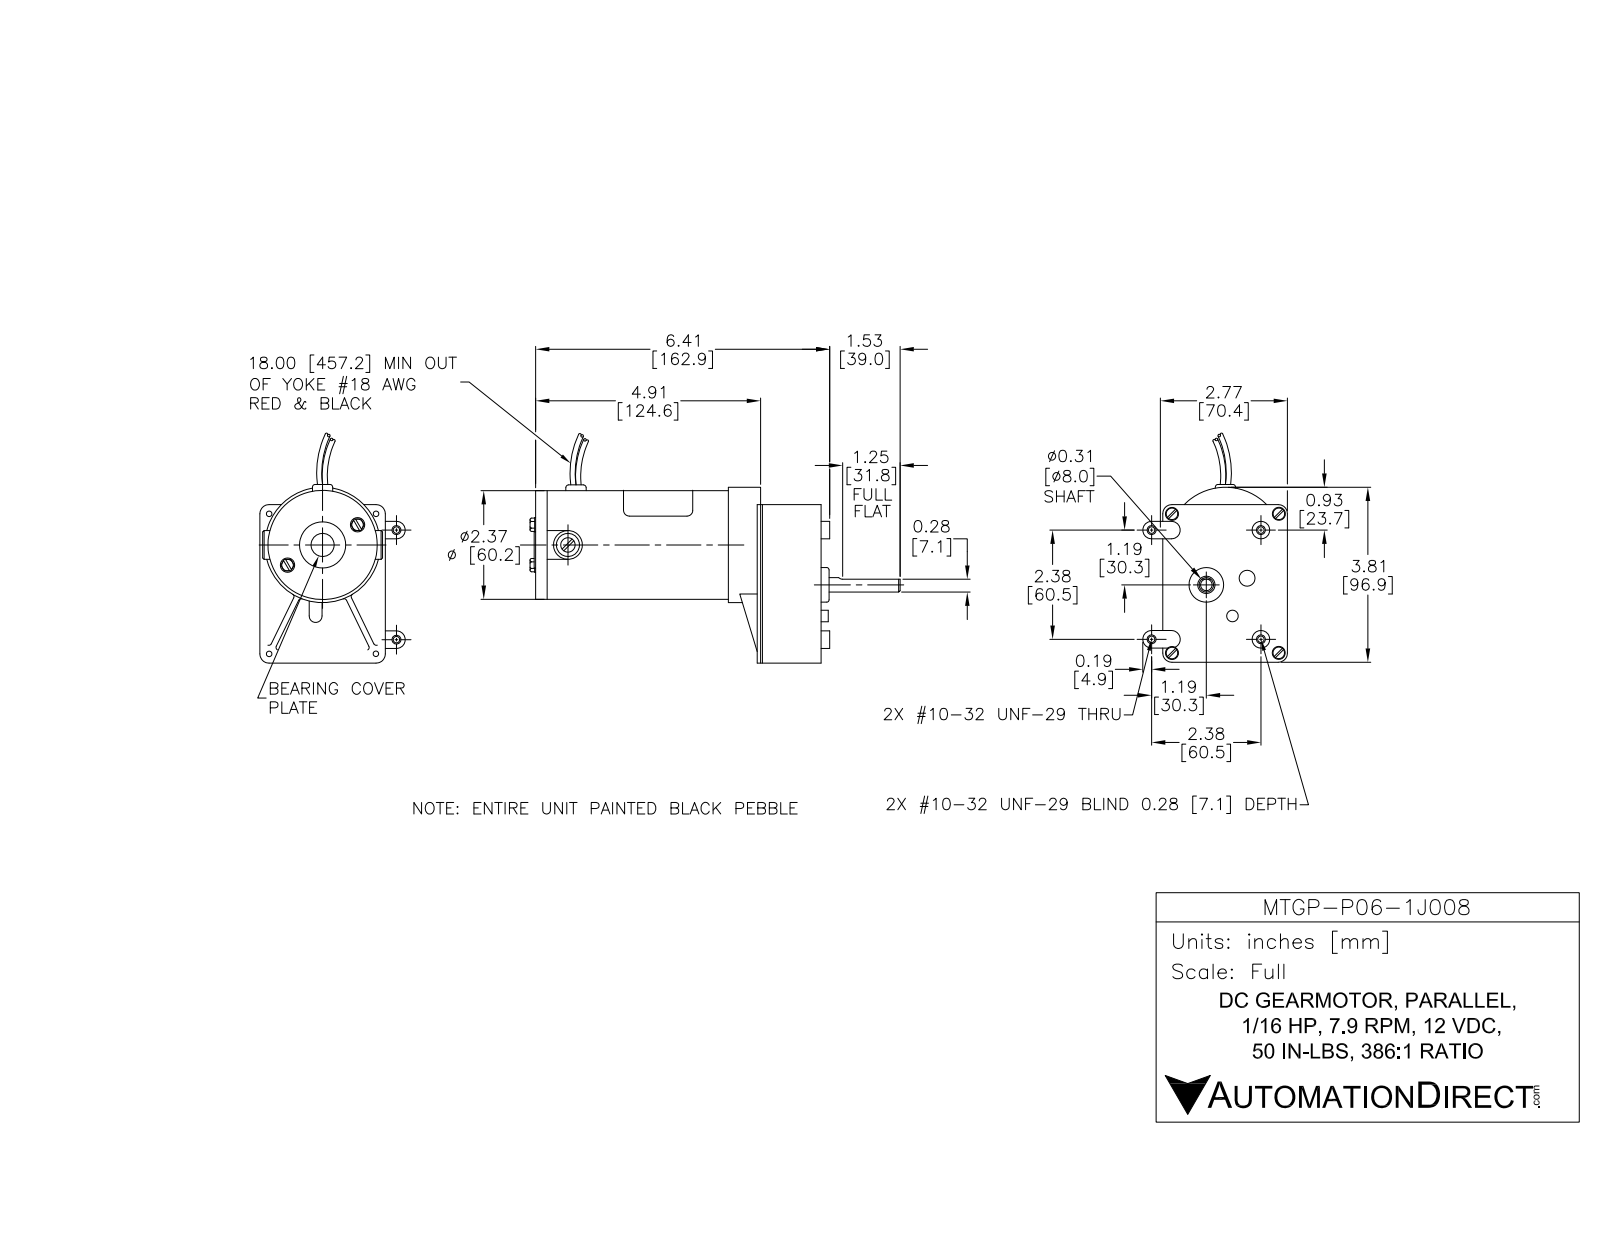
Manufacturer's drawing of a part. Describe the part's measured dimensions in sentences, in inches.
The part is named "MTGP-P06-1J008". Its 3-D file was written by "SolidWorks 2016 (AUTOMOTIVE_DESIGN)". It is 27 solids with 266 faces: 115 planar, 130 cylindrical and 21 other. Overall it measures 7.922 by 5.092 by 3.181 inches. Its volume is 20.18 cubic inches and its surface area 156.4 square inches. Round holes: 5 of diameter 0.194, 4 of diameter 0.063, 4 of diameter 0.283, 2 of diameter 0.156, 1 of diameter 0.25, 1 of diameter 0.312, 1 of diameter 0.562, 1 of diameter 1, 1 of diameter 2.25. Round bosses or shafts: 4 of diameter 0.312, 2 of diameter 0.38, 2 of diameter 0.1, 1 of diameter 2.46, 1 of diameter 2.375, 1 of diameter 0.75, 1 of diameter 0.625, 1 of diameter 0.625. Partial cylindrical surfaces (rounded edges, fillets, slot ends): 10 of radius 0.031, 4 of radius 0.1, 4 of radius 0.19, 2 of radius 0.25, 1 of radius 0.134, 1 of radius 0.141, 1 of radius 1.222. The main face-to-face distances are 1.4, 0.25, 4.833, 6.233, 4.583, 5.983, 4.194, 3.944, 0.639, 2.039. The hole center spacings are 1.223, 1.729, 0.373, 0.44, 0.875, 1.306, 1.332, 1.539.
